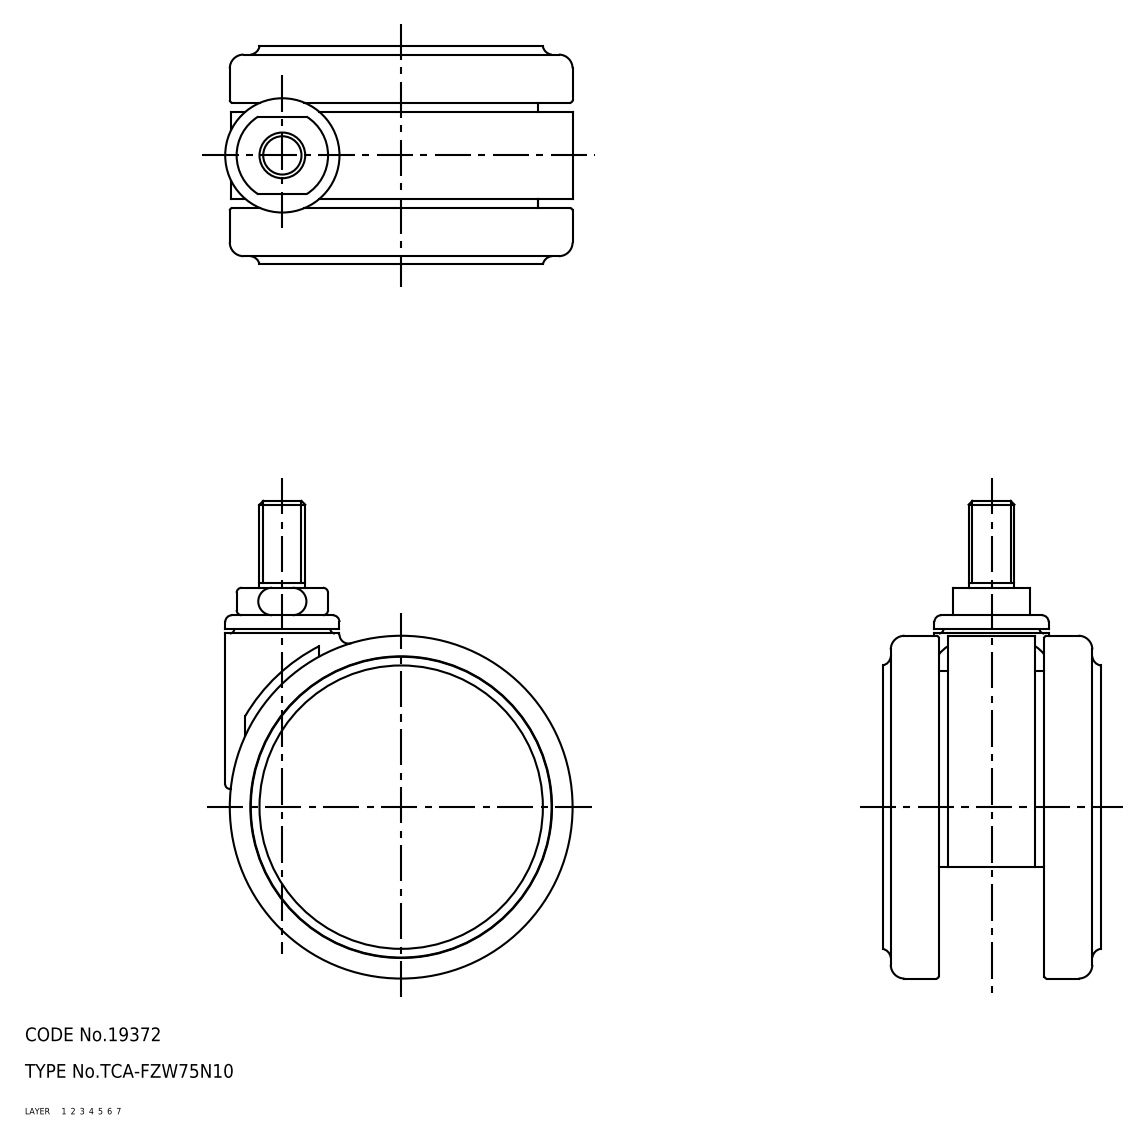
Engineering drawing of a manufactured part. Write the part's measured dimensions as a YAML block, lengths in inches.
part_name: "TCA-FZW75N10; caster"
step_written_by: "SolidWorks 2015 (AUTOMOTIVE_DESIGN)"
units: inches
bodies: {solids: 1, faces: 1801, planar: 425, cylindrical: 766, other: 610}
overall_size: [4.114, 2.992, 1.878]
volume: 6.903
surface_area: 106.7
round_holes:
  - {diameter: 0.256, count: 1}
  - {diameter: 0.315, count: 1}
  - {diameter: 0.319, count: 1}
  - {diameter: 0.335, count: 1}
  - {diameter: 0.402, count: 1}
  - {diameter: 0.433, count: 1}
  - {diameter: 0.669, count: 1}
  - {diameter: 0.713, count: 1}
  - {diameter: 0.748, count: 1}
  - {diameter: 0.89, count: 1}
  - {diameter: 2.323, count: 1}
  - {diameter: 2.48, count: 1}
round_bosses_or_shafts:
  - {diameter: 0.63, count: 2}
  - {diameter: 2.591, count: 1}
  - {diameter: 2.126, count: 1}
  - {diameter: 1.024, count: 1}
  - {diameter: 0.984, count: 1}
  - {diameter: 0.551, count: 1}
  - {diameter: 0.394, count: 1}
  - {diameter: 0.315, count: 1}
partial_cylinders:
  - {radius: 0.039, count: 139}
  - {radius: 0.02, count: 133}
  - {radius: 0.012, count: 120}
  - {radius: 0.008, count: 16}
  - {radius: 0.079, count: 12}
  - {radius: 0.118, count: 1}
  - {radius: 0.157, count: 1}
  - {radius: 0.236, count: 1}
face_to_face_distances: [0.059, 1.819, 0.071, 0.13, 1.748, 1.689, 1.264, 0.354, 0.484, 1.394]
